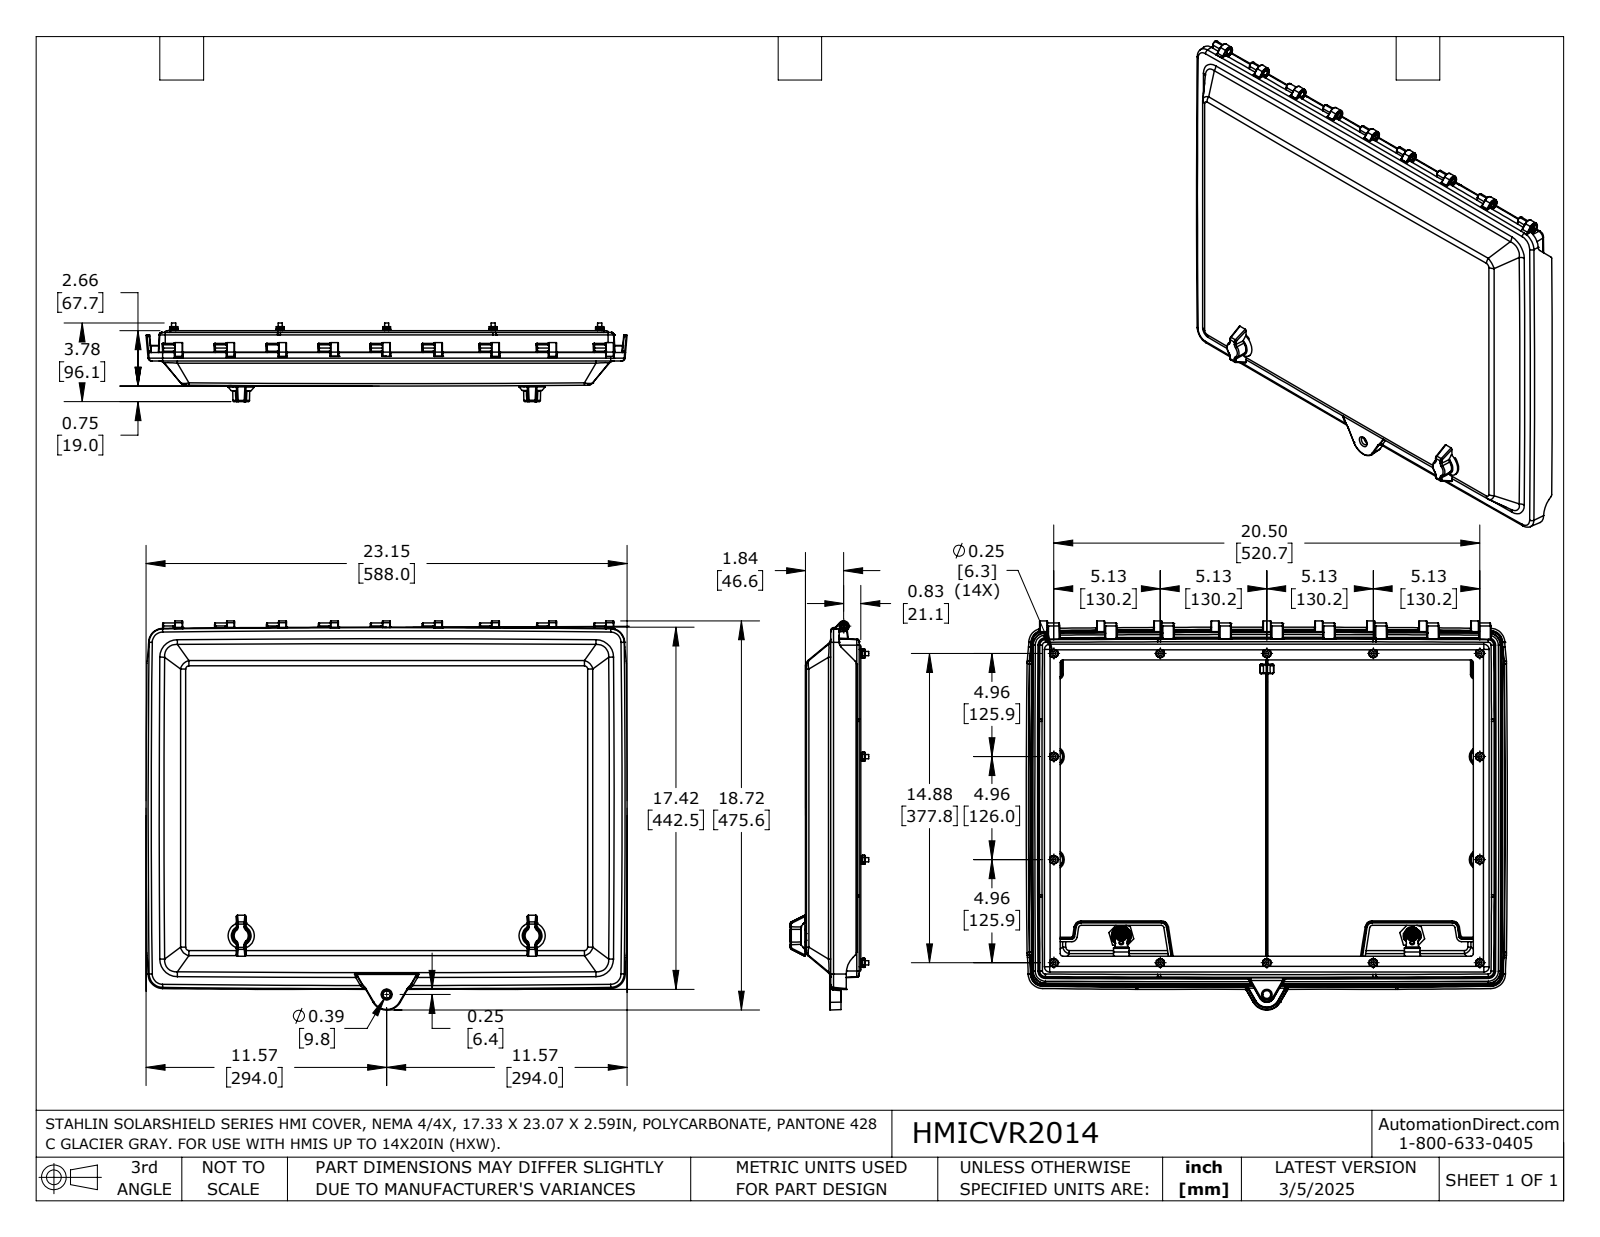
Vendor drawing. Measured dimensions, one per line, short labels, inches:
name: HMICVR2014
written by: SolidWorks 2024 (AUTOMOTIVE_DESIGN)
unit: in
bodies: 74 solids, 3461 faces (1128 planar, 810 cylindrical, 1523 other)
size: 23.148 × 18.724 × 3.783
volume: 147.2 in³; area: 2 278 in²
holes: 16× ⌀0.197, 14× ⌀0.25, 13× ⌀0.19, 2× ⌀0.083, 2× ⌀0.168, 2× ⌀0.201, 2× ⌀0.236, 2× ⌀0.315, 2× ⌀0.591, 2× ⌀0.802, 2× ⌀0.846, 1× ⌀0.328
bosses: 14× ⌀0.394, 14× ⌀0.373, 14× ⌀0.2, 2× ⌀1.26, 2× ⌀0.78, 2× ⌀0.531, 2× ⌀0.37, 2× ⌀0.3
rounds: 143× R0.02, 76× R0.03, 60× R0.012, 40× R0.02, 32× R0.04, 12× R0.01, 12× R0.059, 8× R0.05
face distances: 0.25, 1, 0.125, 1.125, 1.25, 0.125, 1.375, 1.23, 0.98, 0.02
hole spacings: 15.733, 18.065, 10.25, 14.875, 4.957, 5.125, 5.125, 9.917
